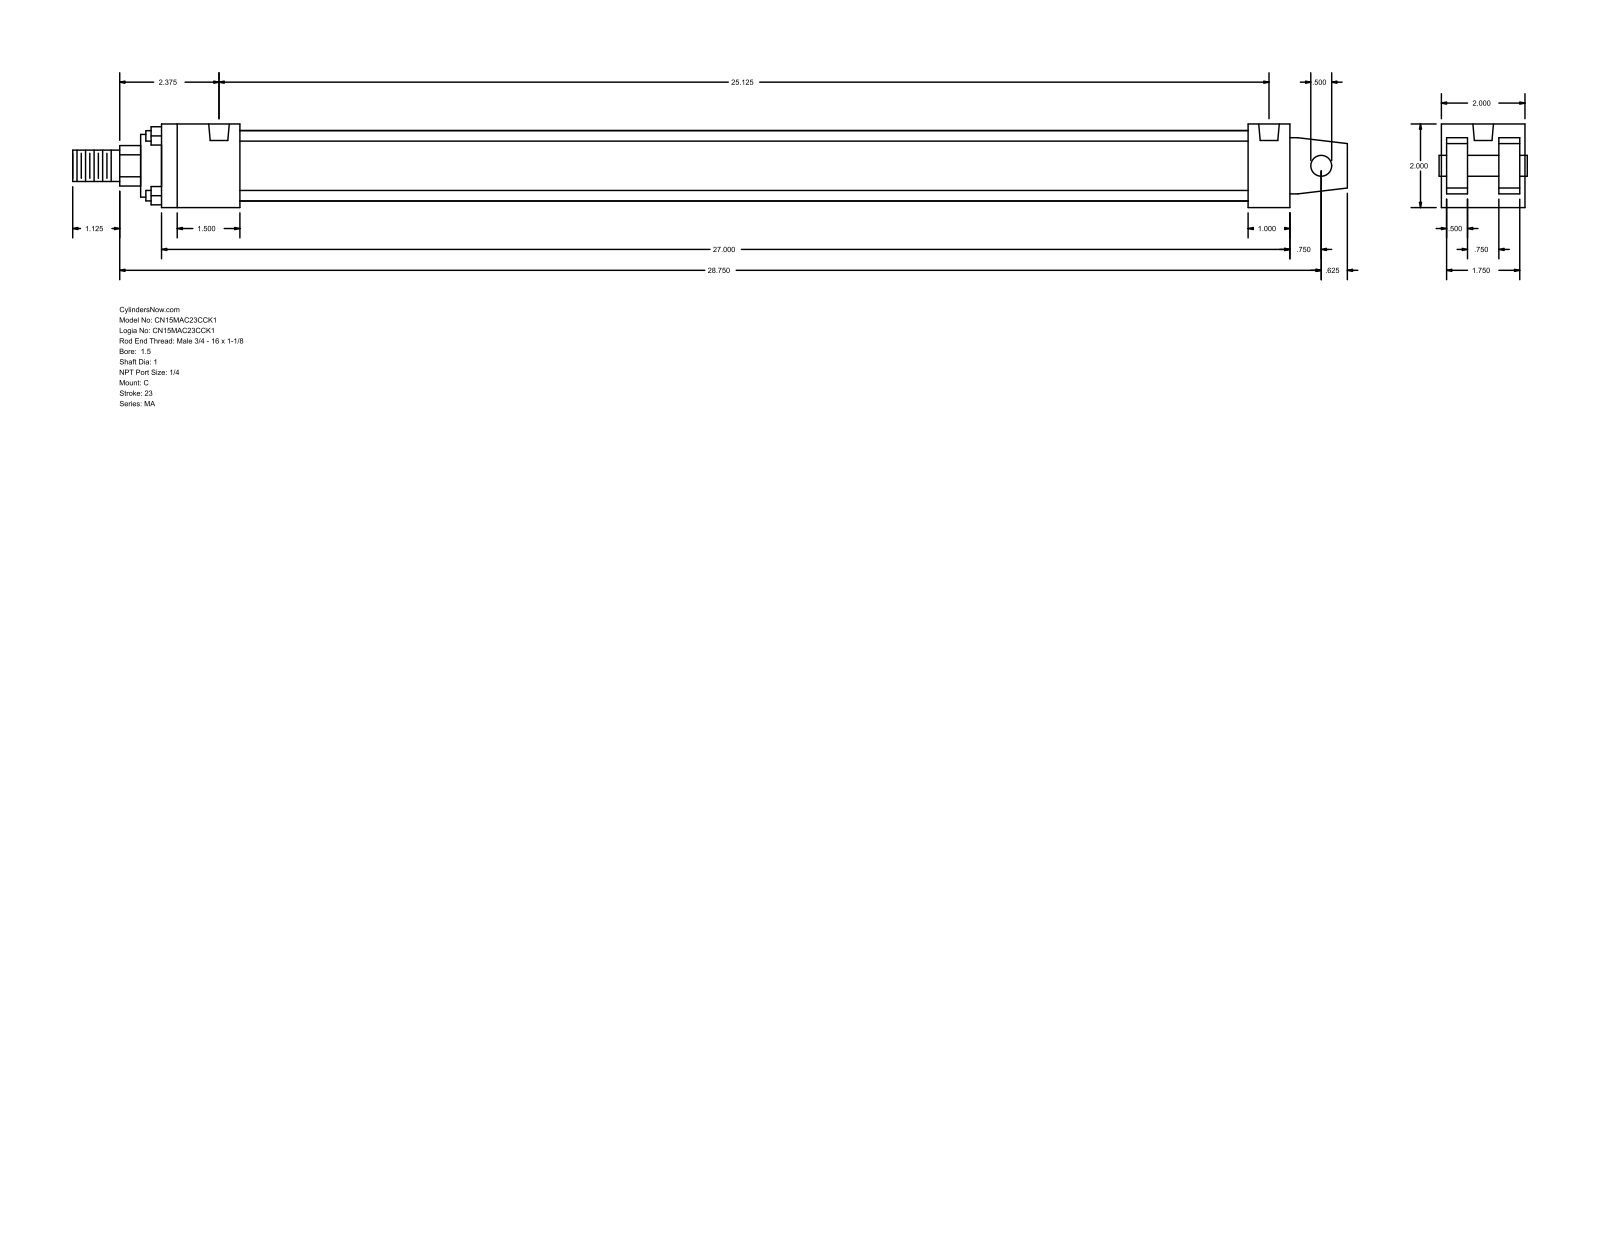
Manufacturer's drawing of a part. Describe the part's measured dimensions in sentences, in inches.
The part is named "MA_C__0150_1". Its 3-D file was written by "GSSL Pune (CONFIG_CONTROL_DESIGN)". It is 0 solids with 103 faces: 76 planar, 27 cylindrical and 0 other. Overall it measures 30.5 by 2 by 2 inches. Round holes: 4 of diameter 0.313, 2 of diameter 0.492. Round bosses or shafts: 4 of diameter 0.25, 1 of diameter 1.69, 1 of diameter 1.5, 1 of diameter 1, 1 of diameter 0.75, 1 of diameter 0.5. Partial cylindrical surfaces (rounded edges, fillets, slot ends): 1 of radius 0.484. The main face-to-face distances are 2, 1.875, 0.5, 0.125, 0.625, 1.375, 1.25, 27, 1, 26. The hole center spacings are 25.125.
